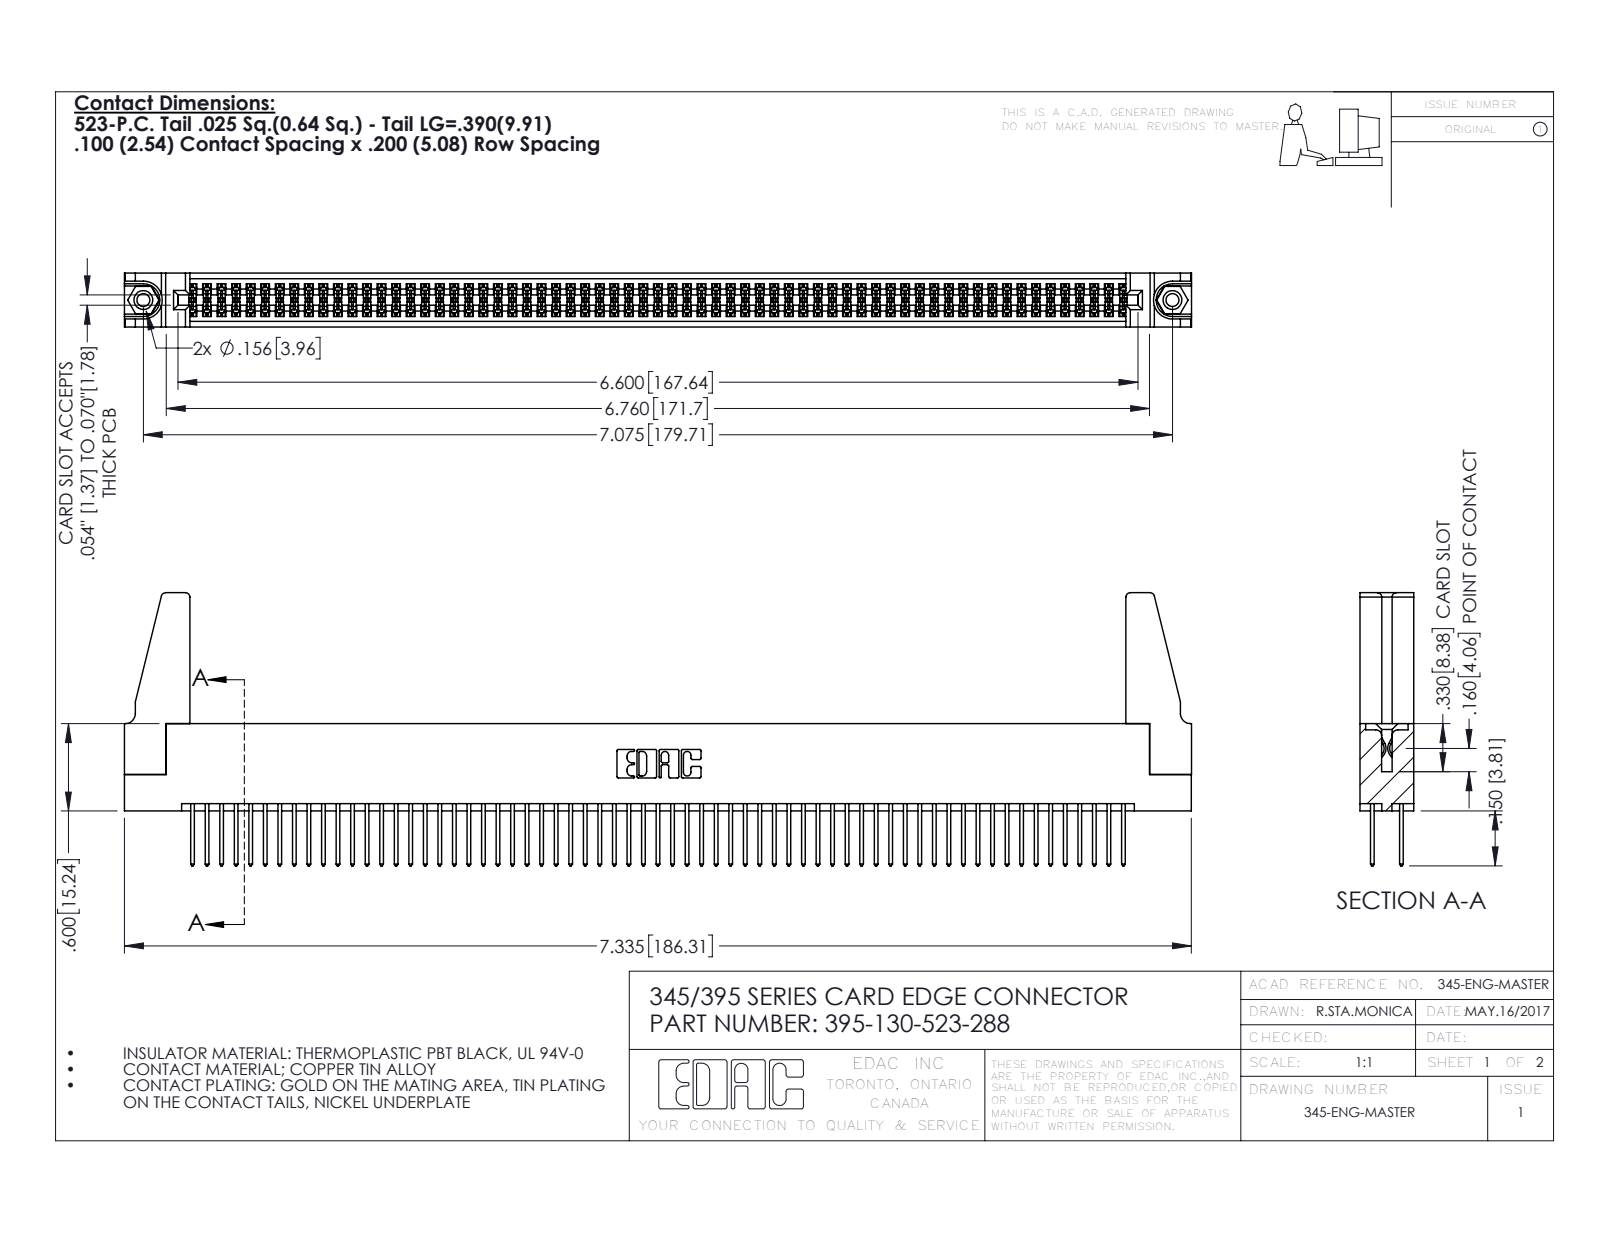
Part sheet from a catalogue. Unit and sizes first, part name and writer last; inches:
Units: inches
Overall size (bounding box): 7.336 × 1.877 × 0.37
Round holes (diameter × count): ⌀0.089 ×2, ⌀0.125 ×2, ⌀0.156 ×2, ⌀0.064 ×1
Round bosses / shafts (diameter × count): ⌀0.155 ×2
Partial cylindrical surfaces — rounded edges, fillets, slot ends (radius × count): R0.006 ×195, R0.01 ×130, R0.01 ×22, R0.03 ×8, R0.007 ×6, R0.031 ×6, R0.026 ×3, R0.014 ×2
Main face-to-face distances: 0.072, 0.298, 0.2, 0.098, 0.272, 0.025, 0.37, 0.225, 0.175, 0.149
Hole centre spacings: 0.27, 6.839, 7.075
Volume: 1.332 in³ · Surface area: 49.95 in²
Bodies: 135 solids, 6750 faces (4442 planar, 2292 cylindrical, 16 other)
Part name (STEP PRODUCT): 345-292-001_345-293-123; 345-250-001_345-250-001-102; 345-220-078_345-220-088; 395-130-523-288 (+1 more)
STEP written by: SolidWorks 2016 (CONFIG_CONTROL_DESIGN)
